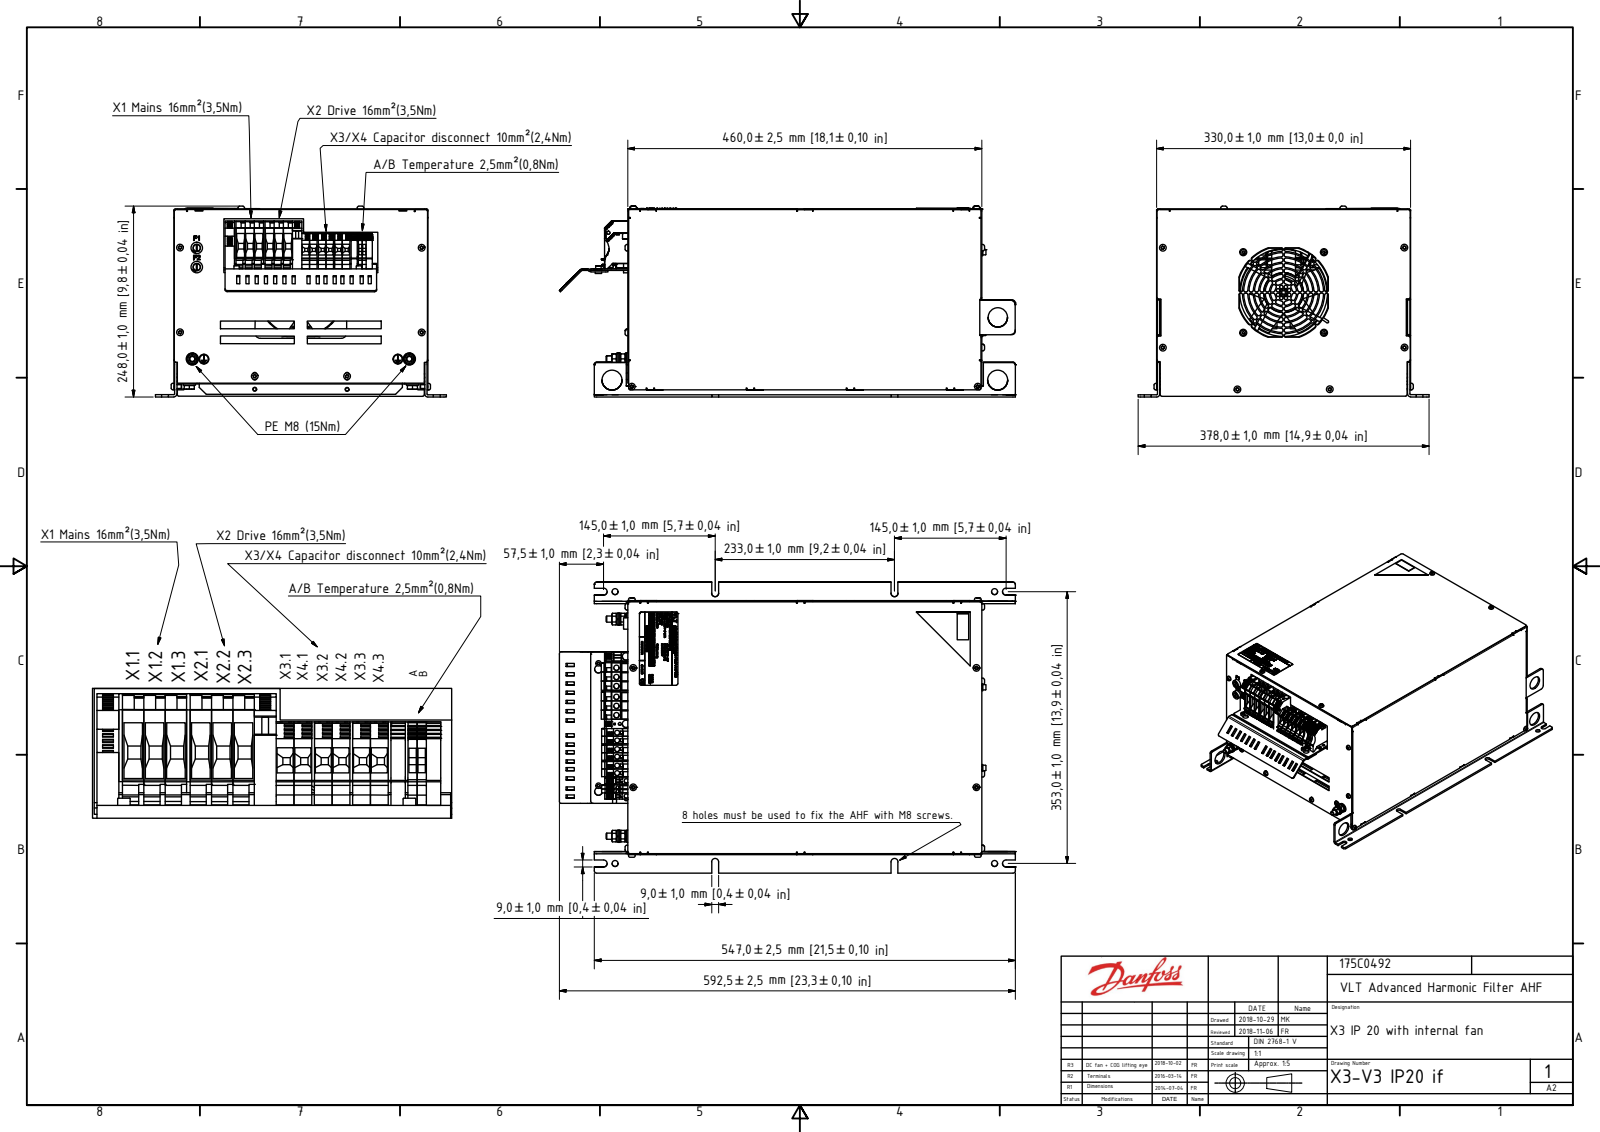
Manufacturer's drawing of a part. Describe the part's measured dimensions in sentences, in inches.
The part is named "X3.3 IP20 if". Its 3-D file was written by "Autodesk Inventor 2018 (AUTOMOTIVE_DESIGN)". It is 3 solids with 12291 faces: 7766 planar, 2771 cylindrical and 1754 other. Overall it measures 23.327 by 14.882 by 9.766 inches. Its volume is 130 cubic inches and its surface area 2 895 square inches. Round holes: 17 of diameter 0.128, 17 of diameter 0.268, 12 of diameter 0.197, 12 of diameter 0.217, 12 of diameter 0.249, 12 of diameter 0.335, 8 of diameter 0.323, 8 of diameter 0.331, 6 of diameter 0.157, 5 of diameter 0.097, 4 of diameter 0.167, 4 of diameter 0.169. Round bosses or shafts: 26 of diameter 0.335, 24 of diameter 0.177, 14 of diameter 0.197, 8 of diameter 0.63, 8 of diameter 0.583, 8 of diameter 0.449, 8 of diameter 0.315, 8 of diameter 0.288. Partial cylindrical surfaces (rounded edges, fillets, slot ends): 328 of radius 0.079, 200 of radius 0.02, 156 of radius 0.045, 122 of radius 0.012, 104 of radius 0.012, 71 of radius 0.03, 61 of radius 0.004, 52 of radius 0.012. The main face-to-face distances are 0.039, 0.118, 12.953, 5.827, 18.071, 12.992, 8.917, 8.957, 8.799, 8.839. The hole center spacings are 11.417, 1.811, 2.917, 4.126, 7.598, 11.614, 19.724, 10.005.
